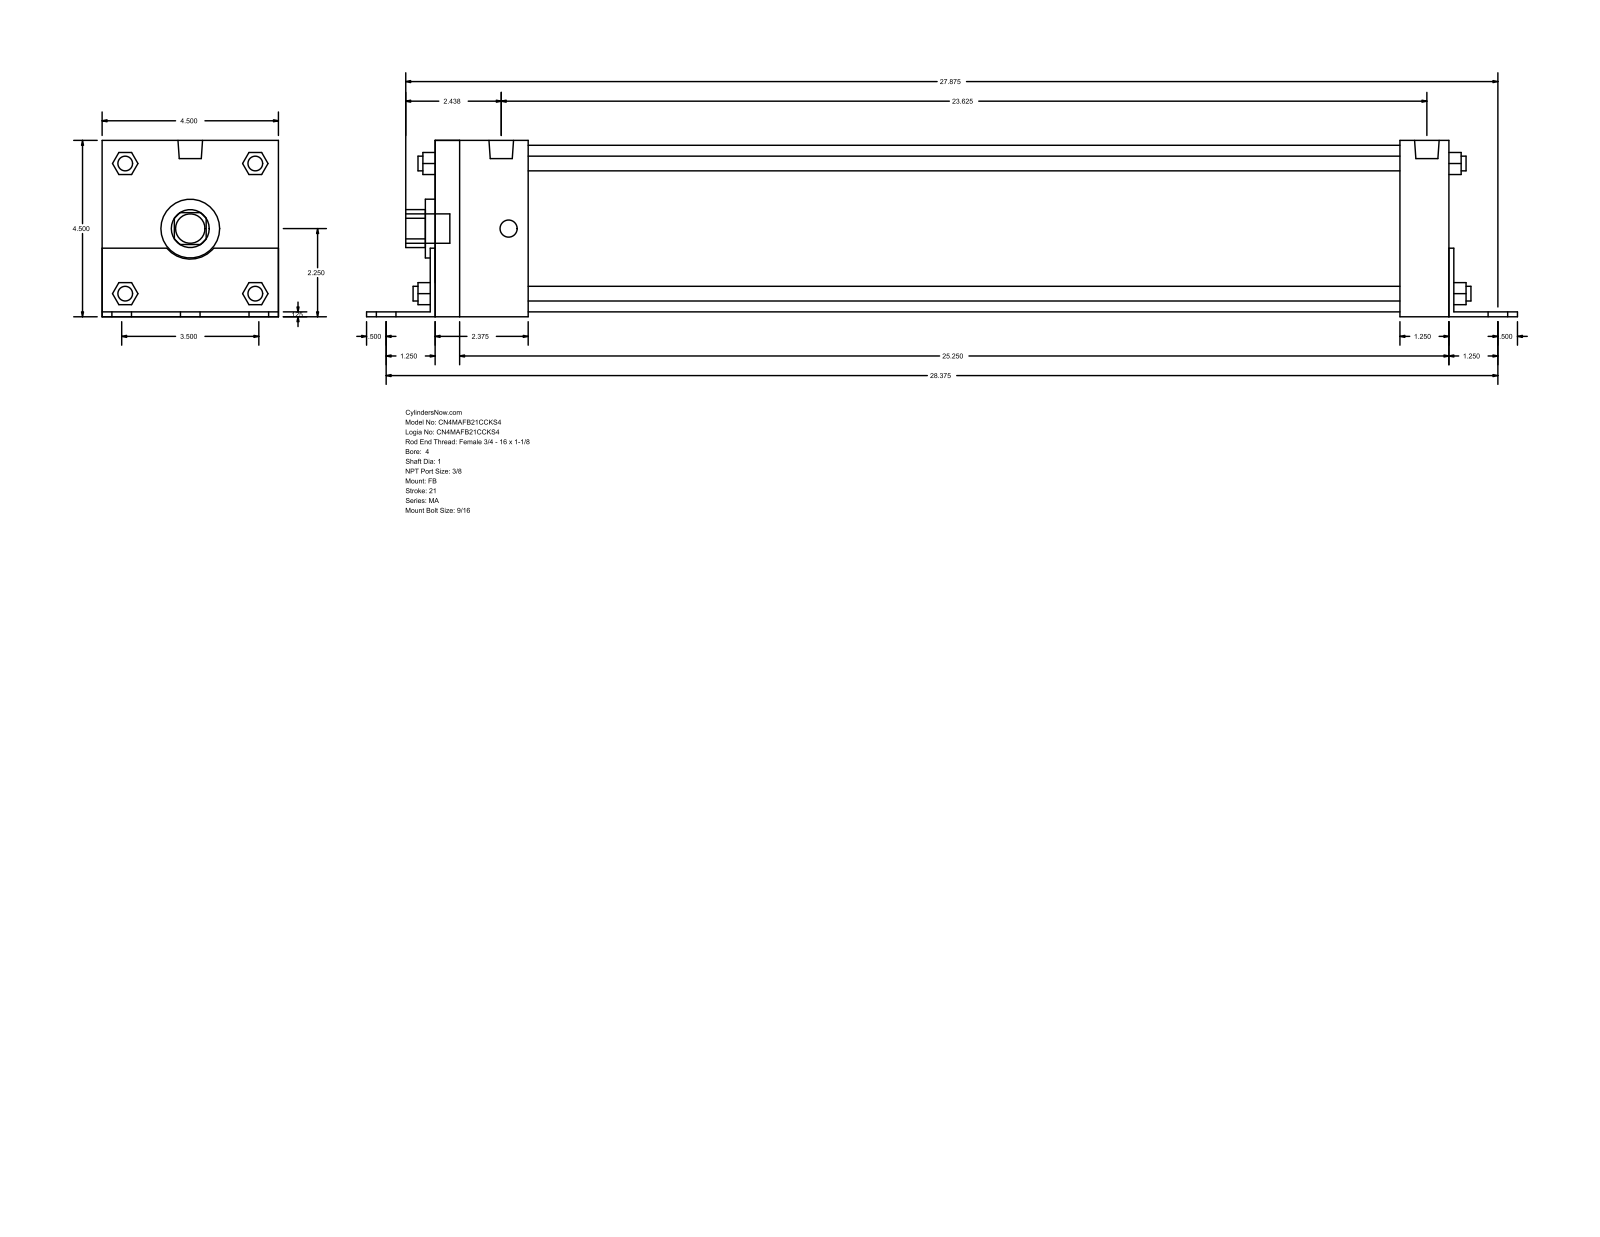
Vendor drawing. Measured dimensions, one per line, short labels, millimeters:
name: MA_FB__0400_1
written by: GSSL Pune (CONFIG_CONTROL_DESIGN)
unit: mm
bodies: 0 solids, 140 faces (105 planar, 35 cylindrical, 0 other)
size: 746.12 × 114.35 × 114.3
holes: 1× ⌀25.4, 1× ⌀38.1, 1× ⌀107.95
bosses: 6× ⌀14.29, 4× ⌀11.11, 4× ⌀9.53, 2× ⌀15.93, 1× ⌀19.05
rounds: 1× R12.29, 1× R19.81
face distances: 114.3, 3.17, 114.35, 3.12, 111.18, 657.22, 3.18, 663.57, 660.4, 660.39
